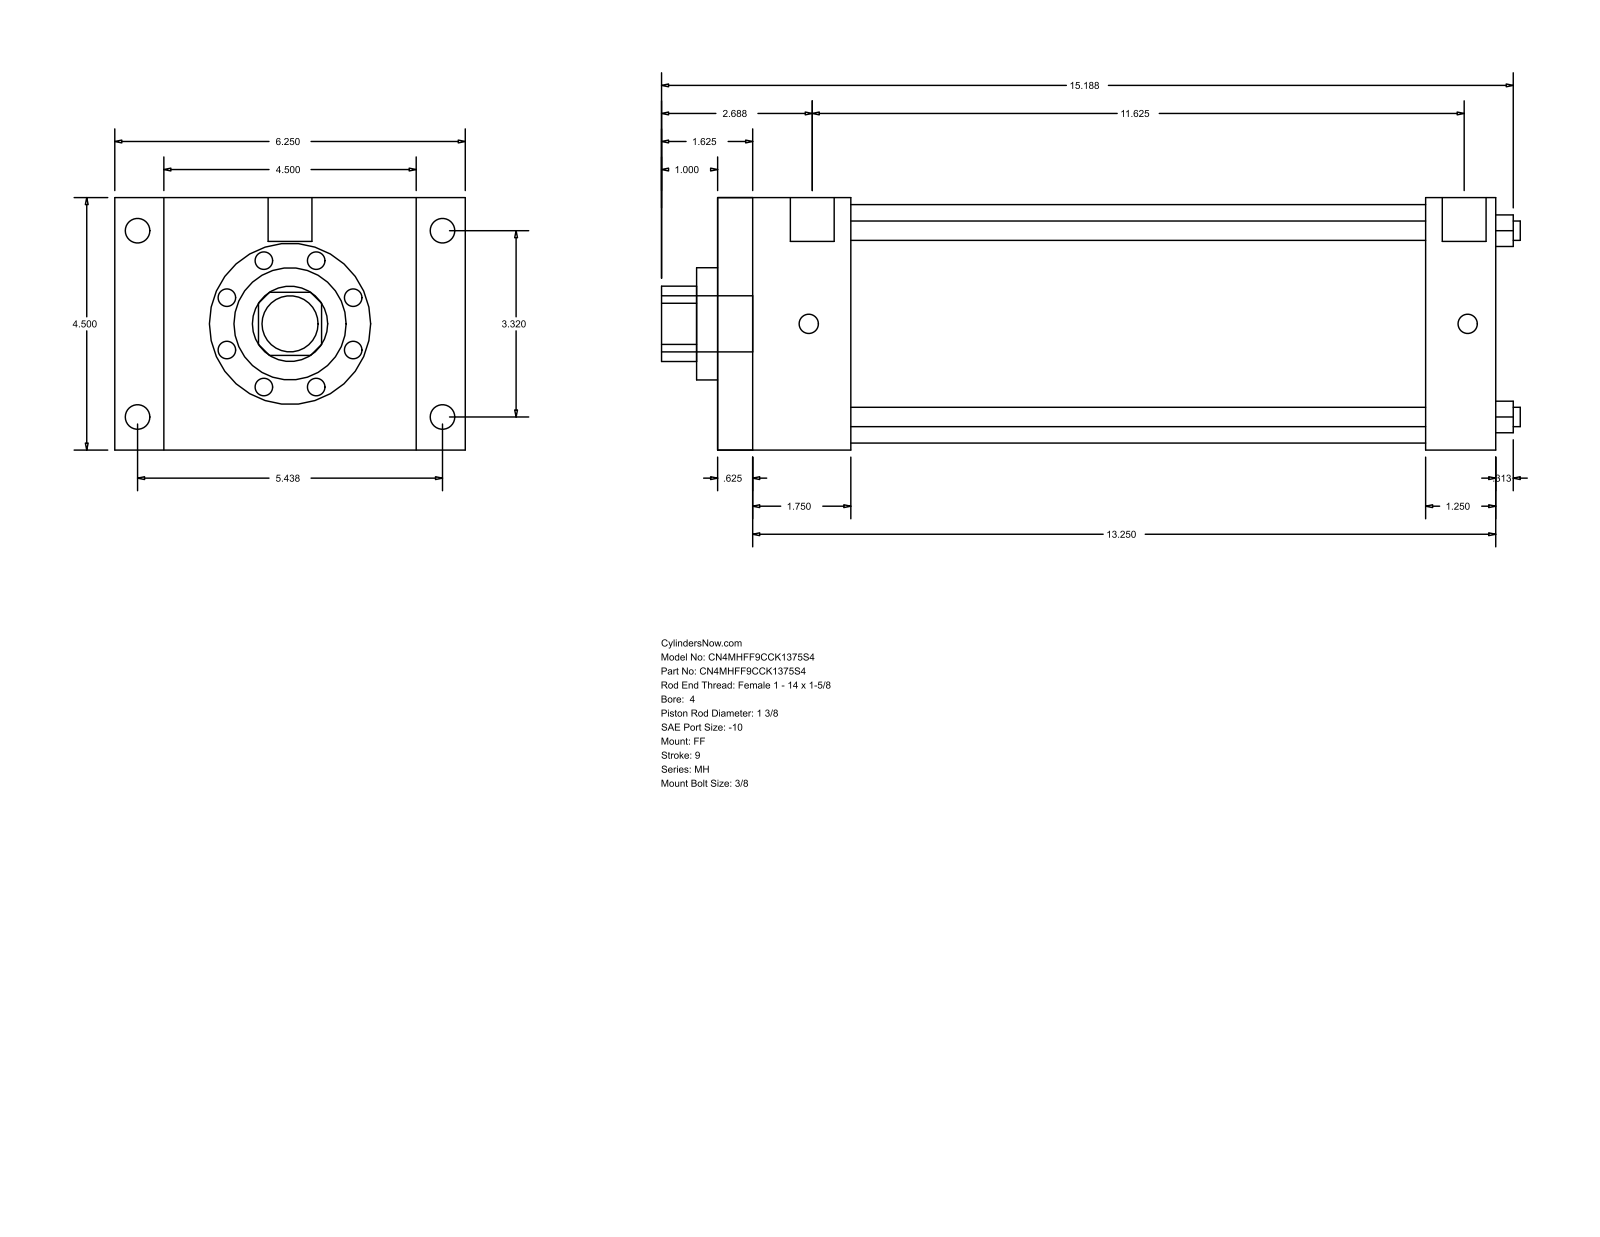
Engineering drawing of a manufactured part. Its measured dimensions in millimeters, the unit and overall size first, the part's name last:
Units: millimetres
Overall size (bounding box): 388.94 × 158.75 × 114.3
Round holes (diameter × count): ⌀8.76 ×4, ⌀34.92 ×1, ⌀50.8 ×1, ⌀107.95 ×1
Round bosses / shafts (diameter × count): ⌀11.13 ×4, ⌀8.73 ×4, ⌀19.84 ×2, ⌀25.4 ×1
Partial cylindrical surfaces — rounded edges, fillets, slot ends (radius × count): R17.06 ×1
Main face-to-face distances: 114.3, 352.42, 15.87, 336.55, 60.32, 44.45, 292.1, 320.67, 304.8, 260.35
Hole centre spacings: 59.62, 84.32, 119.25
Bodies: 0 solids, 92 faces (64 planar, 28 cylindrical, 0 other)
Part name (STEP PRODUCT): MH_FF__0400_1.375
STEP written by: GSSL Pune (CONFIG_CONTROL_DESIGN)
